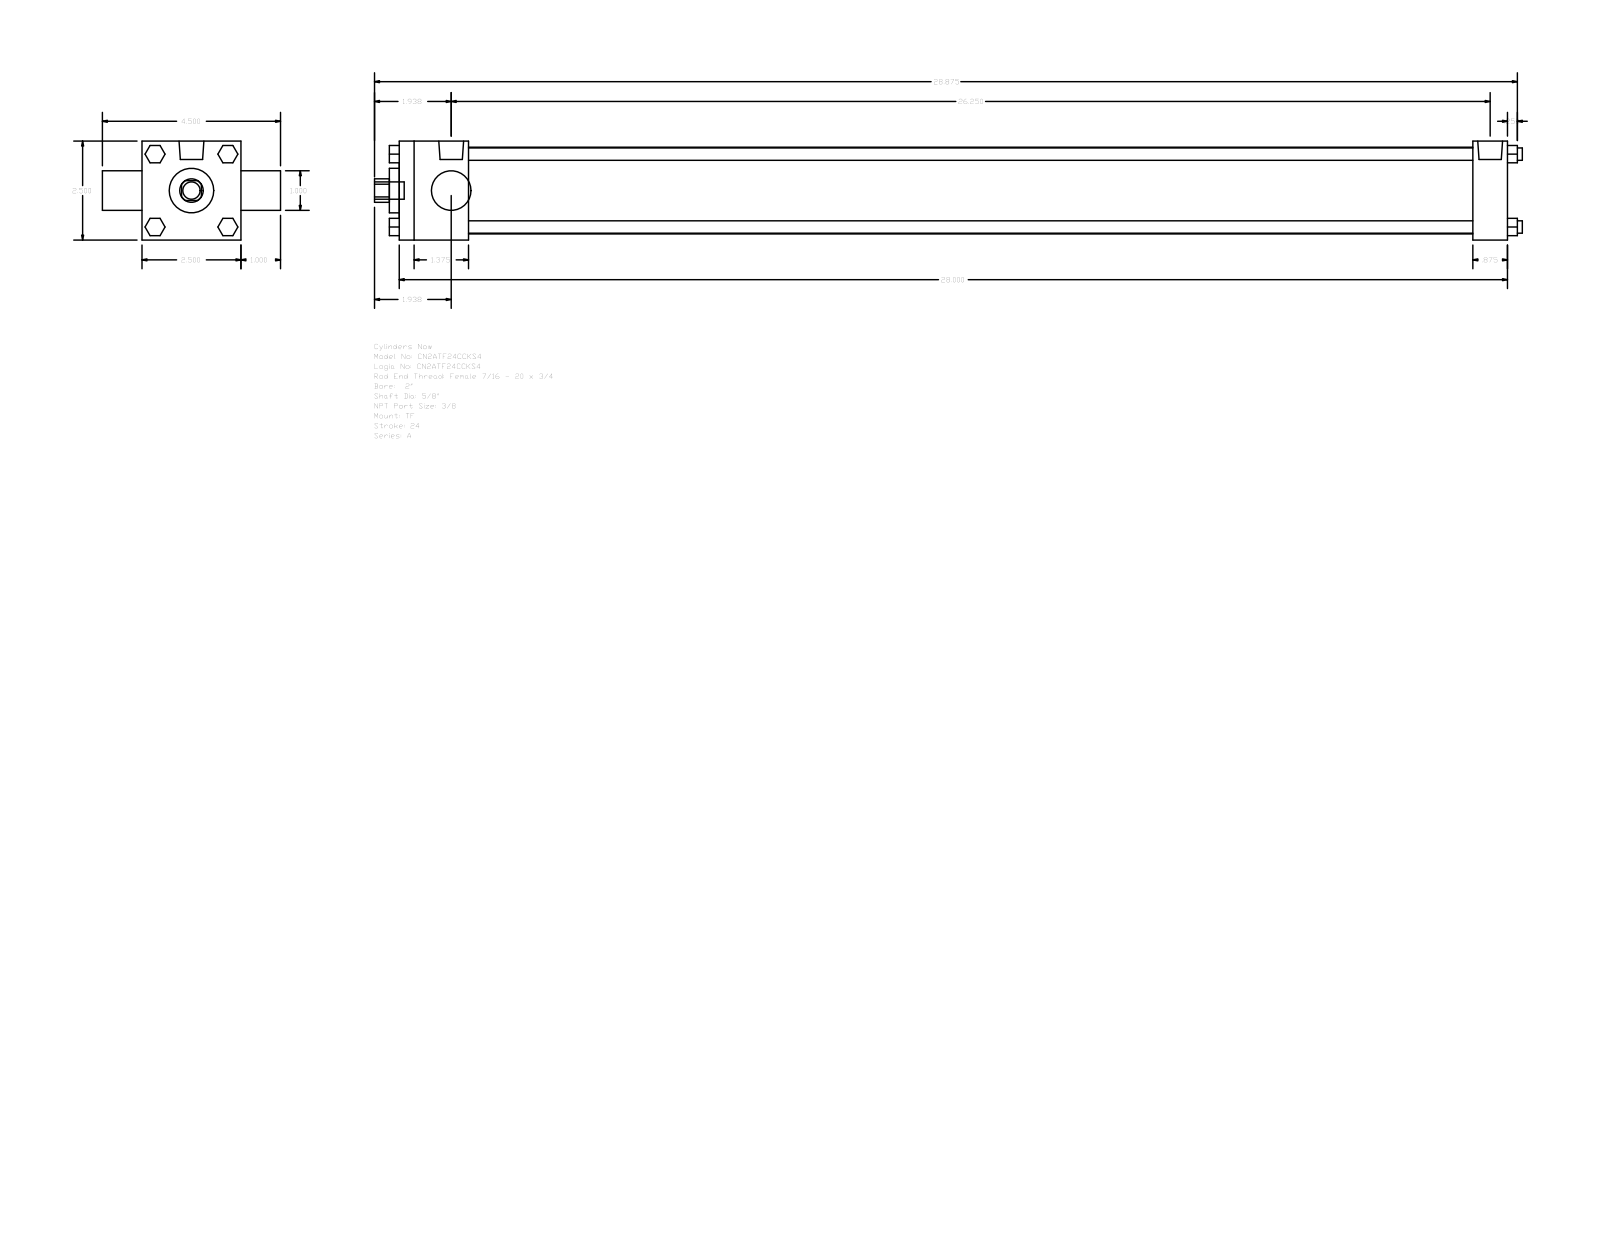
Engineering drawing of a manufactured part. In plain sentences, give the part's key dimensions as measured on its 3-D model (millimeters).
The part is named "A_TF__0200_0.625". Its 3-D file was written by "GSSL Pune (CONFIG_CONTROL_DESIGN)". It is 0 solids with 120 faces: 92 planar, 28 cylindrical and 0 other. Overall it measures 736.6 by 114.3 by 63.5 millimeters. Round holes: 1 of diameter 15.88, 1 of diameter 25.4, 1 of diameter 28.57, 1 of diameter 55.63. Round bosses or shafts: 4 of diameter 7.94, 3 of diameter 5.56, 2 of diameter 15.93, 1 of diameter 11.11. Partial cylindrical surfaces (rounded edges, fillets, slot ends): 1 of radius 7.54. The main face-to-face distances are 63.5, 711.2, 44.45, 688.97, 644.52, 666.75, 22.23, 25.4, 88.9, 50.8.
